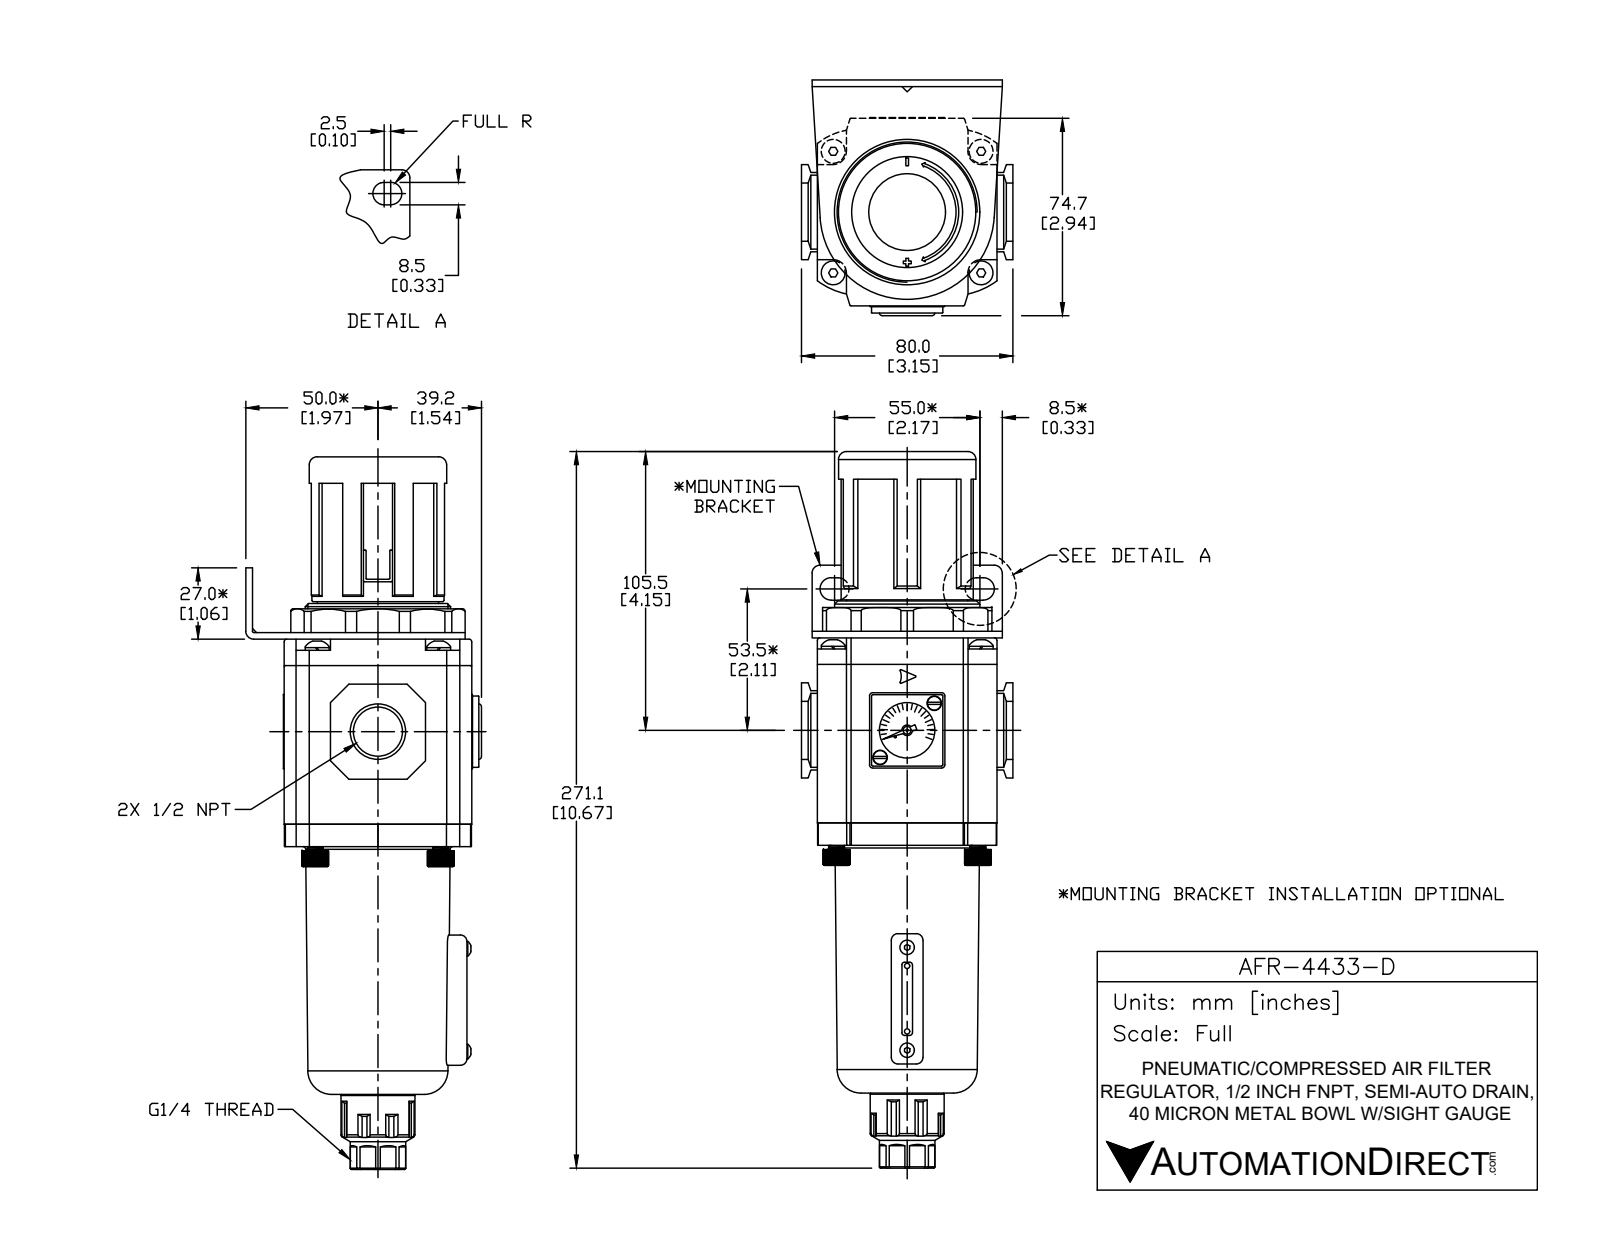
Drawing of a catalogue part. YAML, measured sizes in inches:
part_name: "AFR-4433-D"
step_written_by: "SolidWorks 2015 (CONFIG_CONTROL_DESIGN)"
units: inches
bodies: {solids: 16, faces: 683, planar: 417, cylindrical: 177, other: 89}
overall_size: [10.614, 3.472, 3.15]
volume: 45.83
surface_area: 163.3
round_holes:
  - {diameter: 0.118, count: 6}
  - {diameter: 0.079, count: 1}
  - {diameter: 0.472, count: 1}
  - {diameter: 0.703, count: 1}
  - {diameter: 0.827, count: 1}
  - {diameter: 1.181, count: 1}
round_bosses_or_shafts:
  - {diameter: 0.394, count: 4}
  - {diameter: 0.354, count: 4}
  - {diameter: 0.217, count: 2}
  - {diameter: 0.106, count: 2}
  - {diameter: 2.165, count: 1}
  - {diameter: 2.047, count: 1}
  - {diameter: 1.969, count: 1}
  - {diameter: 1.72, count: 1}
partial_cylinders:
  - {radius: 0.039, count: 16}
  - {radius: 0.047, count: 10}
  - {radius: 0.051, count: 8}
  - {radius: 0.098, count: 8}
  - {radius: 0.374, count: 8}
  - {radius: 0.783, count: 8}
  - {radius: 0.02, count: 6}
  - {radius: 0.012, count: 4}
face_to_face_distances: [0.098, 2.756, 2.854, 2.795, 2.677, 2.913, 3.366, 0.335, 3.091, 3.189]
hole_center_spacings: [1.311, 0.571, 1.677, 2.016, 2.622, 1.141]
